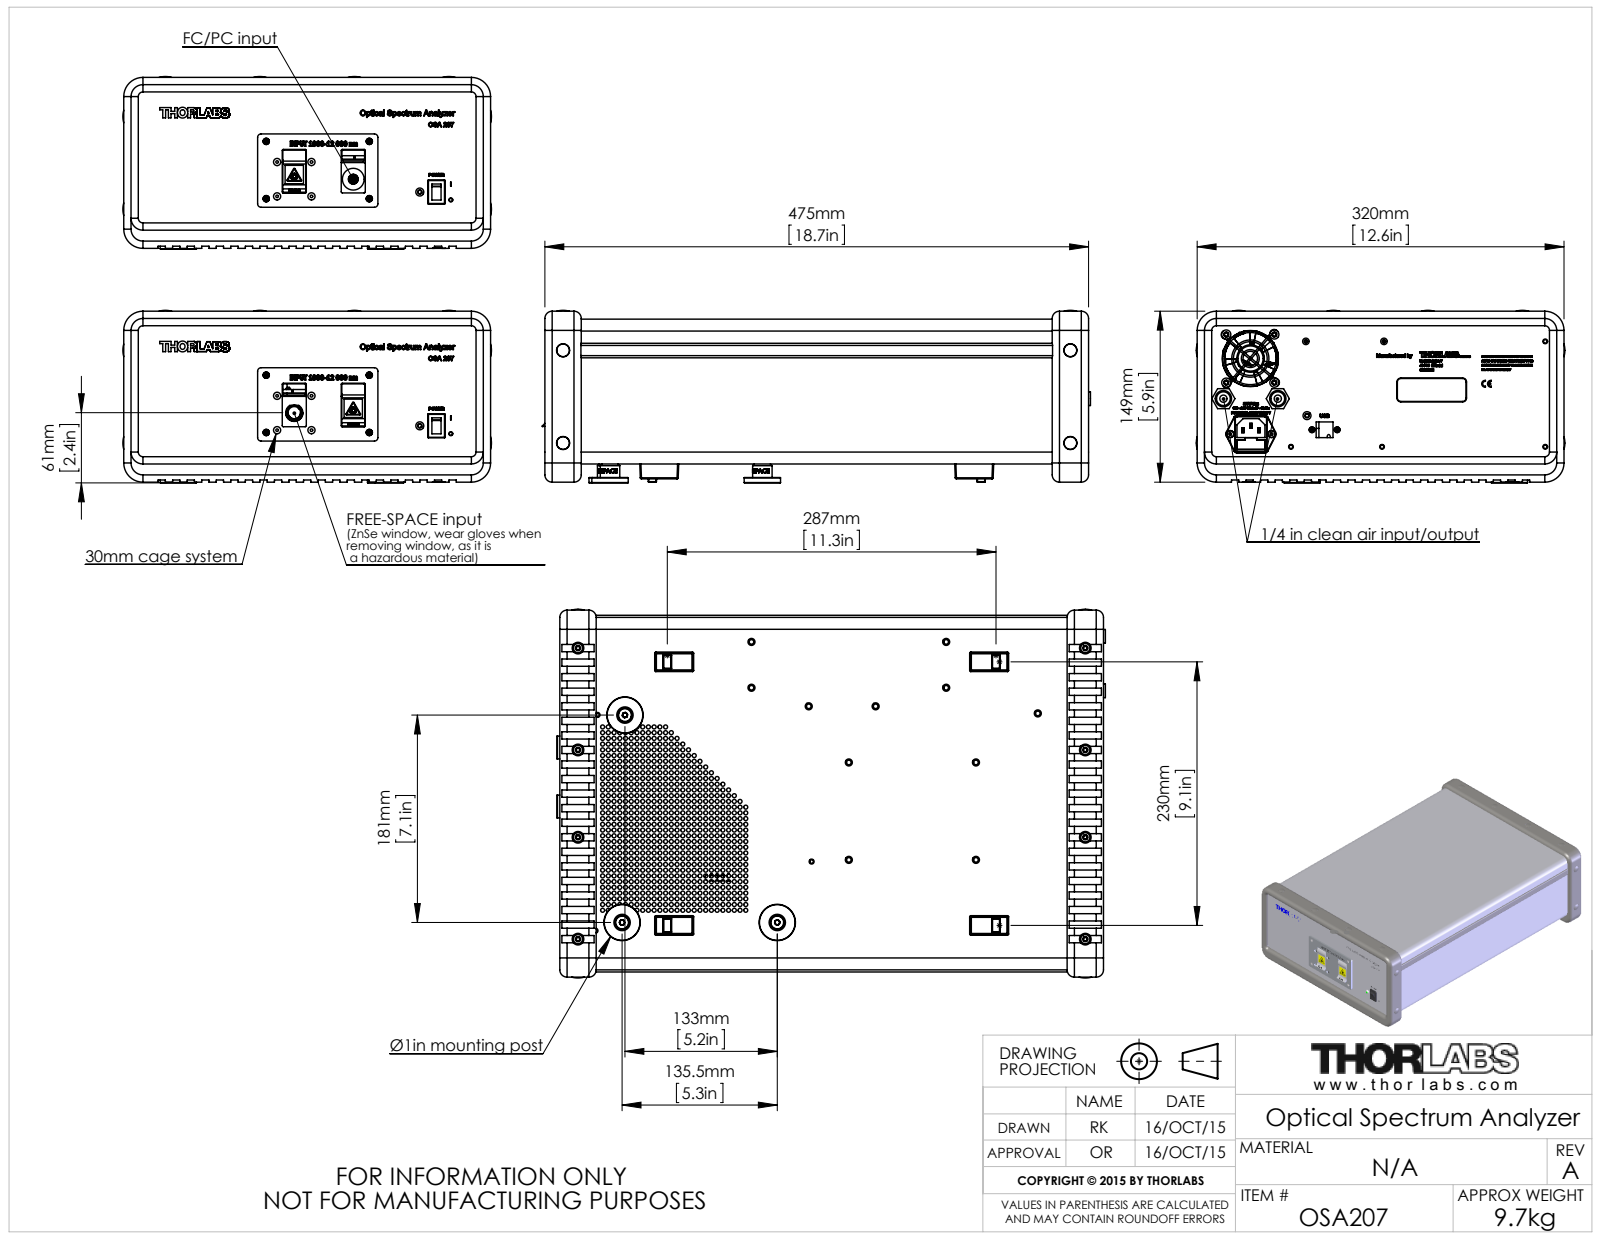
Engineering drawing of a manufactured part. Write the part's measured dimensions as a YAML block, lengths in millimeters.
part_name: "STN012292-E0W"
step_written_by: "SolidWorks 2014 (AUTOMOTIVE_DESIGN)"
units: millimeters
bodies: {solids: 0, faces: 1942, planar: 719, cylindrical: 1057, other: 166}
overall_size: [478.75, 321.82, 150.61]
round_holes:
  - {diameter: 3.5, count: 711}
  - {diameter: 11.43, count: 12}
  - {diameter: 10.16, count: 8}
  - {diameter: 6.3, count: 4}
  - {diameter: 18.5, count: 3}
  - {diameter: 6.35, count: 2}
  - {diameter: 49, count: 1}
round_bosses_or_shafts:
  - {diameter: 11.05, count: 12}
  - {diameter: 12, count: 5}
  - {diameter: 8, count: 4}
  - {diameter: 1.5, count: 4}
  - {diameter: 31.75, count: 3}
  - {diameter: 17, count: 3}
  - {diameter: 5, count: 3}
  - {diameter: 18.4, count: 2}
partial_cylinders:
  - {radius: 0.91, count: 40}
  - {radius: 1, count: 32}
  - {radius: 0.5, count: 22}
  - {radius: 6.35, count: 18}
  - {radius: 0.27, count: 16}
  - {radius: 0.38, count: 9}
  - {radius: 3, count: 6}
  - {radius: 1.9, count: 4}
face_to_face_distances: [1, 125.4, 126.4, 124.4, 306.6, 307.6, 4.8, 3.8, 120.6, 121.6]
hole_center_spacings: [5, 10, 15, 20, 30, 7.07, 25, 11.18]
